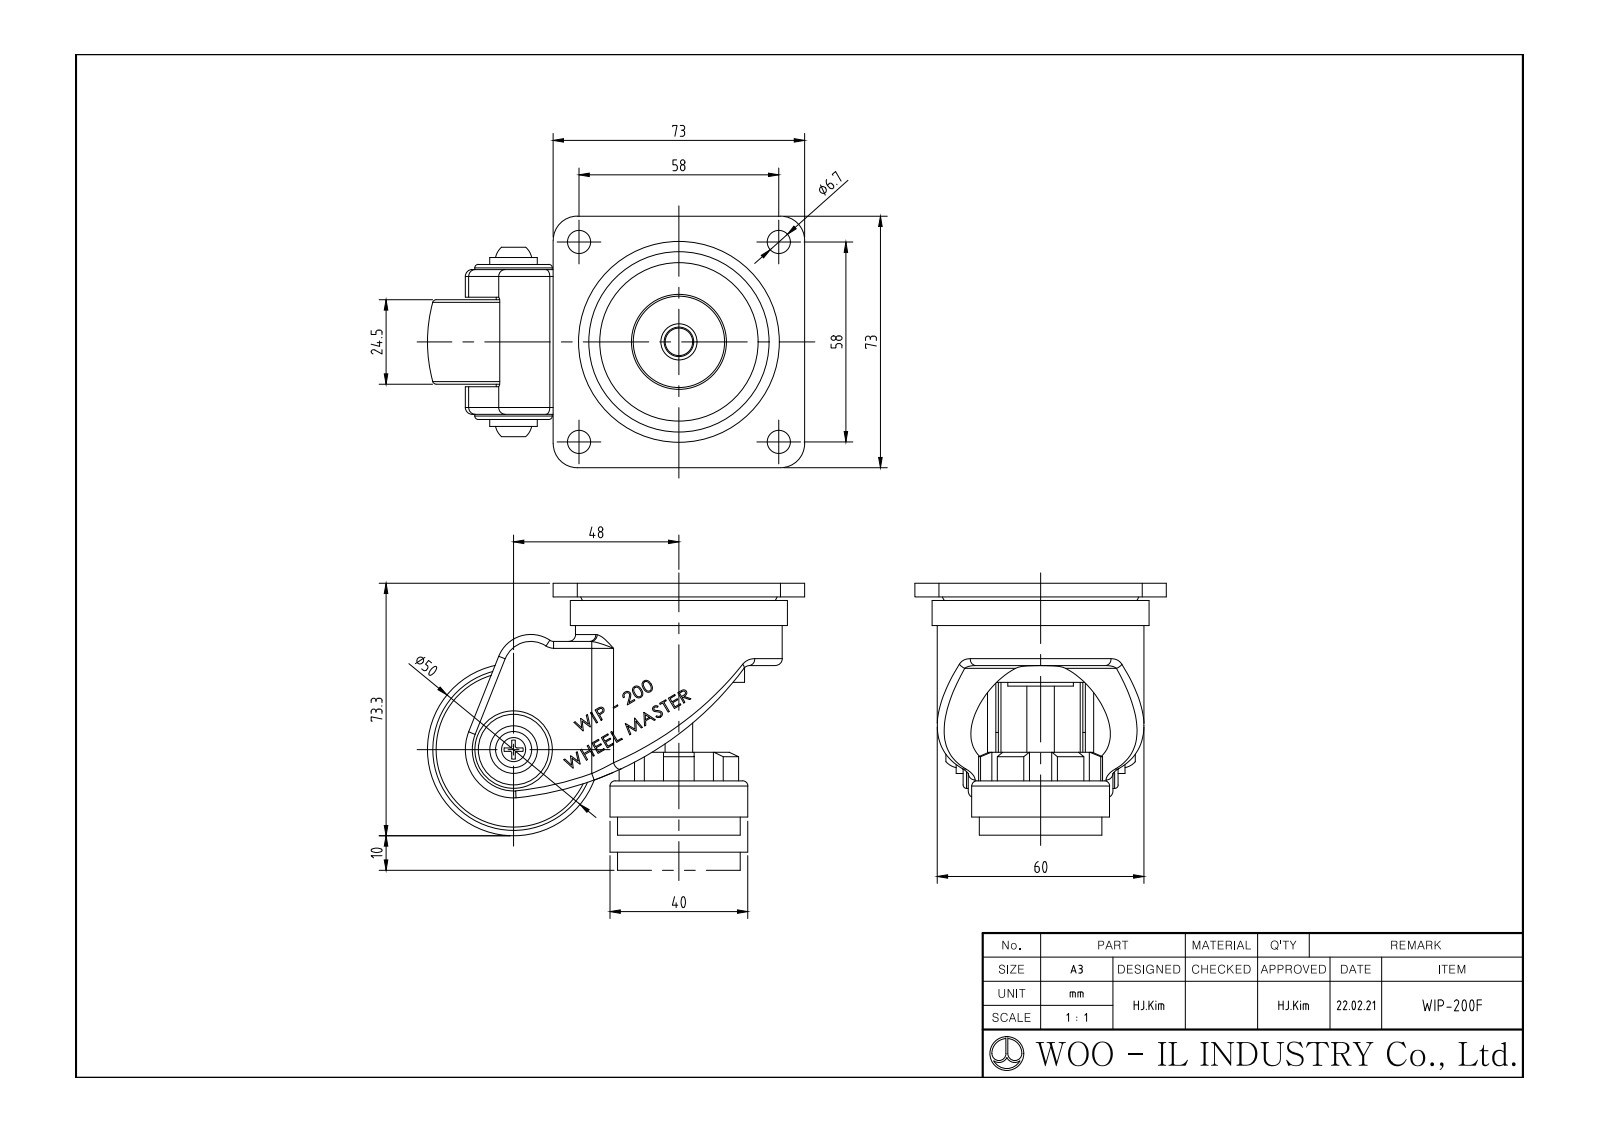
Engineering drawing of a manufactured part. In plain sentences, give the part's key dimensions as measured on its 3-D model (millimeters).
The part is named "WIP-200F". Its 3-D file was written by "SolidWorks 2019 (AUTOMOTIVE_DESIGN)". It is 1 solid with 649 faces: 306 planar, 177 cylindrical and 166 other. Overall it measures 109.5 by 73.3 by 73 millimeters. Its volume is 197 440 cubic millimeters and its surface area 45 365 square millimeters. Round holes: 4 of diameter 6.7, 1 of diameter 10.4, 1 of diameter 22, 1 of diameter 27, 1 of diameter 31.64. Round bosses or shafts: 1 of diameter 63, 1 of diameter 60, 1 of diameter 40, 1 of diameter 38.1, 1 of diameter 35.6, 1 of diameter 29.64, 1 of diameter 26.5, 1 of diameter 25. Partial cylindrical surfaces (rounded edges, fillets, slot ends): 9 of radius 0.3, 8 of radius 2, 6 of radius 7.53, 5 of radius 10, 4 of radius 0.5, 4 of radius 7, 3 of radius 1, 2 of radius 9.5. The main face-to-face distances are 0.75, 25.25, 4, 8, 8.75, 33.25, 34, 24.5, 26, 45.06. The hole center spacings are 41.01, 58, 82.02.
